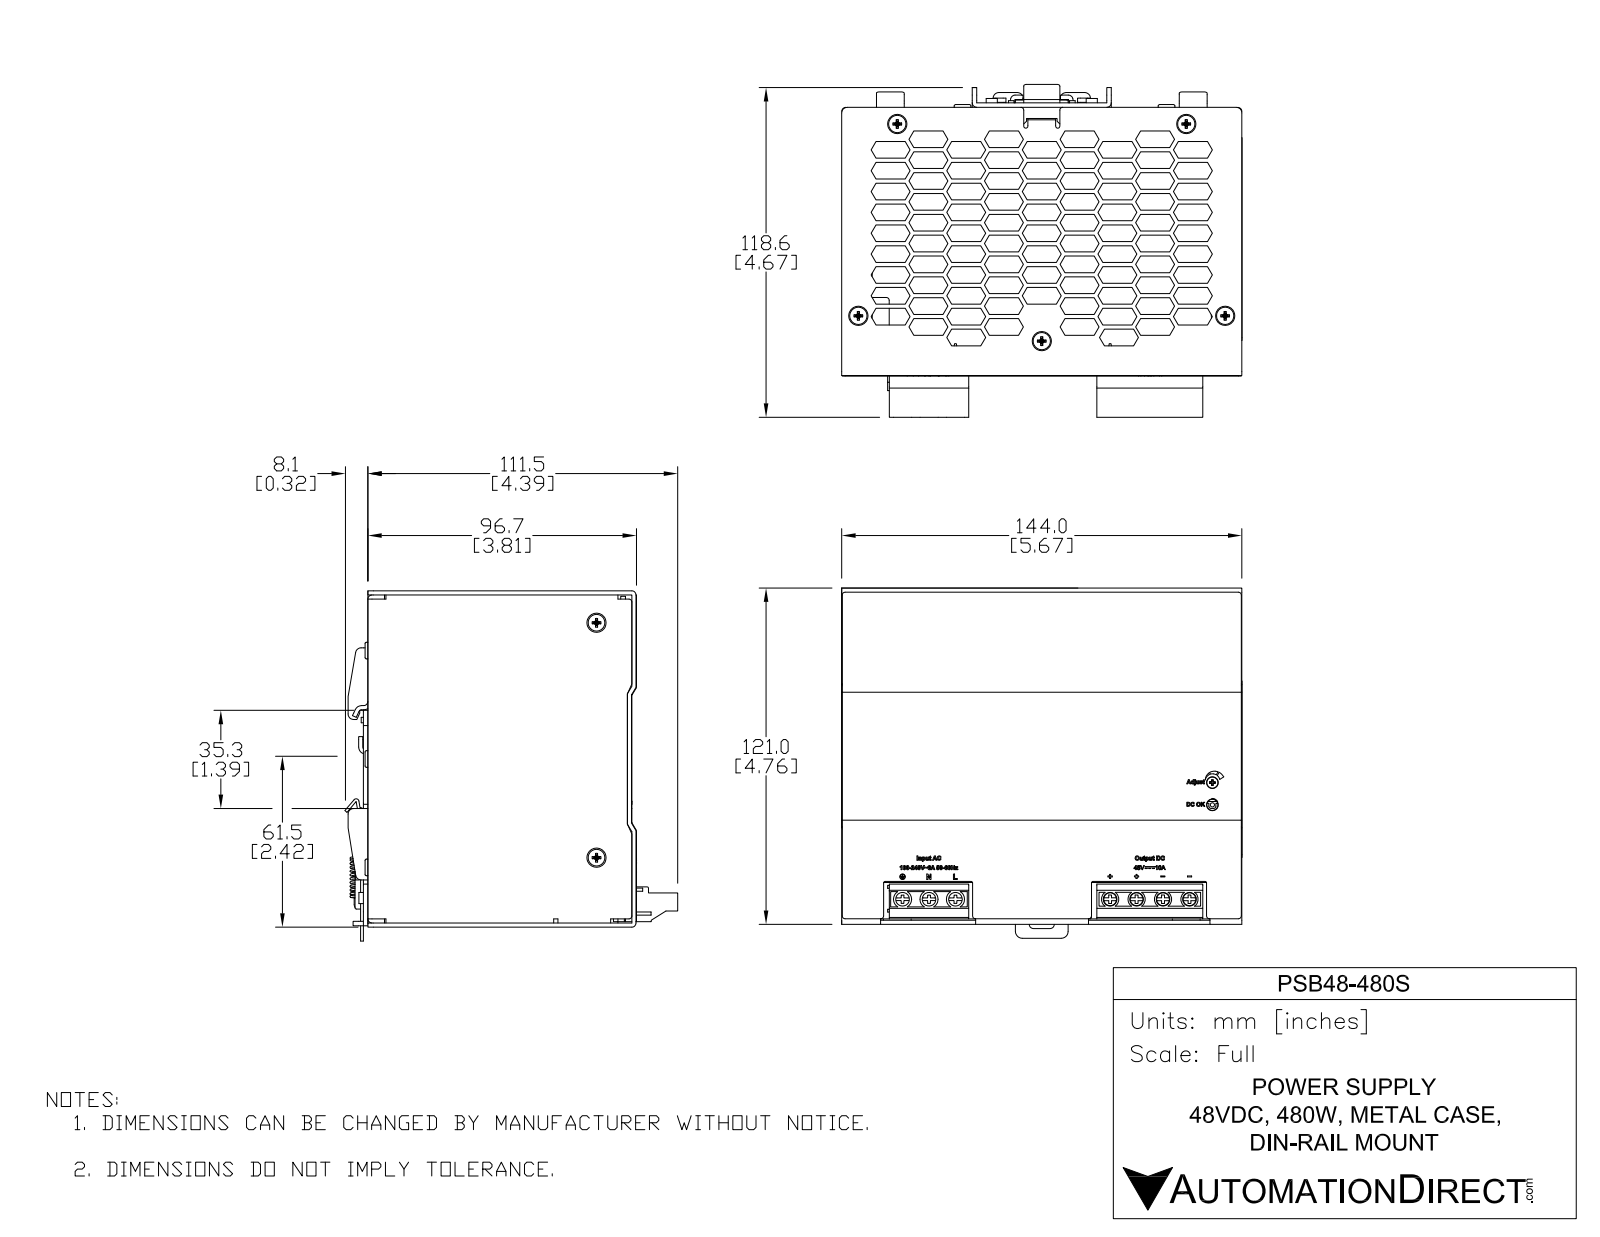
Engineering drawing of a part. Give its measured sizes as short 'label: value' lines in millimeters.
name: PSB48-480S
written by: SolidWorks 2016 (AUTOMOTIVE_DESIGN)
unit: mm
bodies: 62 solids, 4486 faces (3057 planar, 714 cylindrical, 715 other)
size: 144.07 × 126 × 119.1
volume: 188 037 mm³; area: 351 557 mm²
holes: 14× ⌀4.5, 10× ⌀4, 7× ⌀4.6, 7× ⌀4.9, 5× ⌀2, 5× ⌀2.9, 4× ⌀1.6, 4× ⌀2.5, 3× ⌀3.3, 3× ⌀4.1, 3× ⌀7.5, 2× ⌀3
bosses: 10× ⌀6, 8× ⌀3, 7× ⌀0.5, 6× ⌀6.2, 6× ⌀3.5, 5× ⌀5.9, 4× ⌀4.67, 4× ⌀4
rounds: 116× R0.5, 44× R1, 32× R0.75, 17× R1.5, 16× R0.2, 16× R2, 11× R0.9, 7× R0.25
face distances: 1.5, 1.6, 0.43, 6.5, 95, 96.5, 142.5, 90, 93.4, 2.73
hole spacings: 9.52, 74.7, 84.22, 19.04, 7, 8, 12.21, 13
